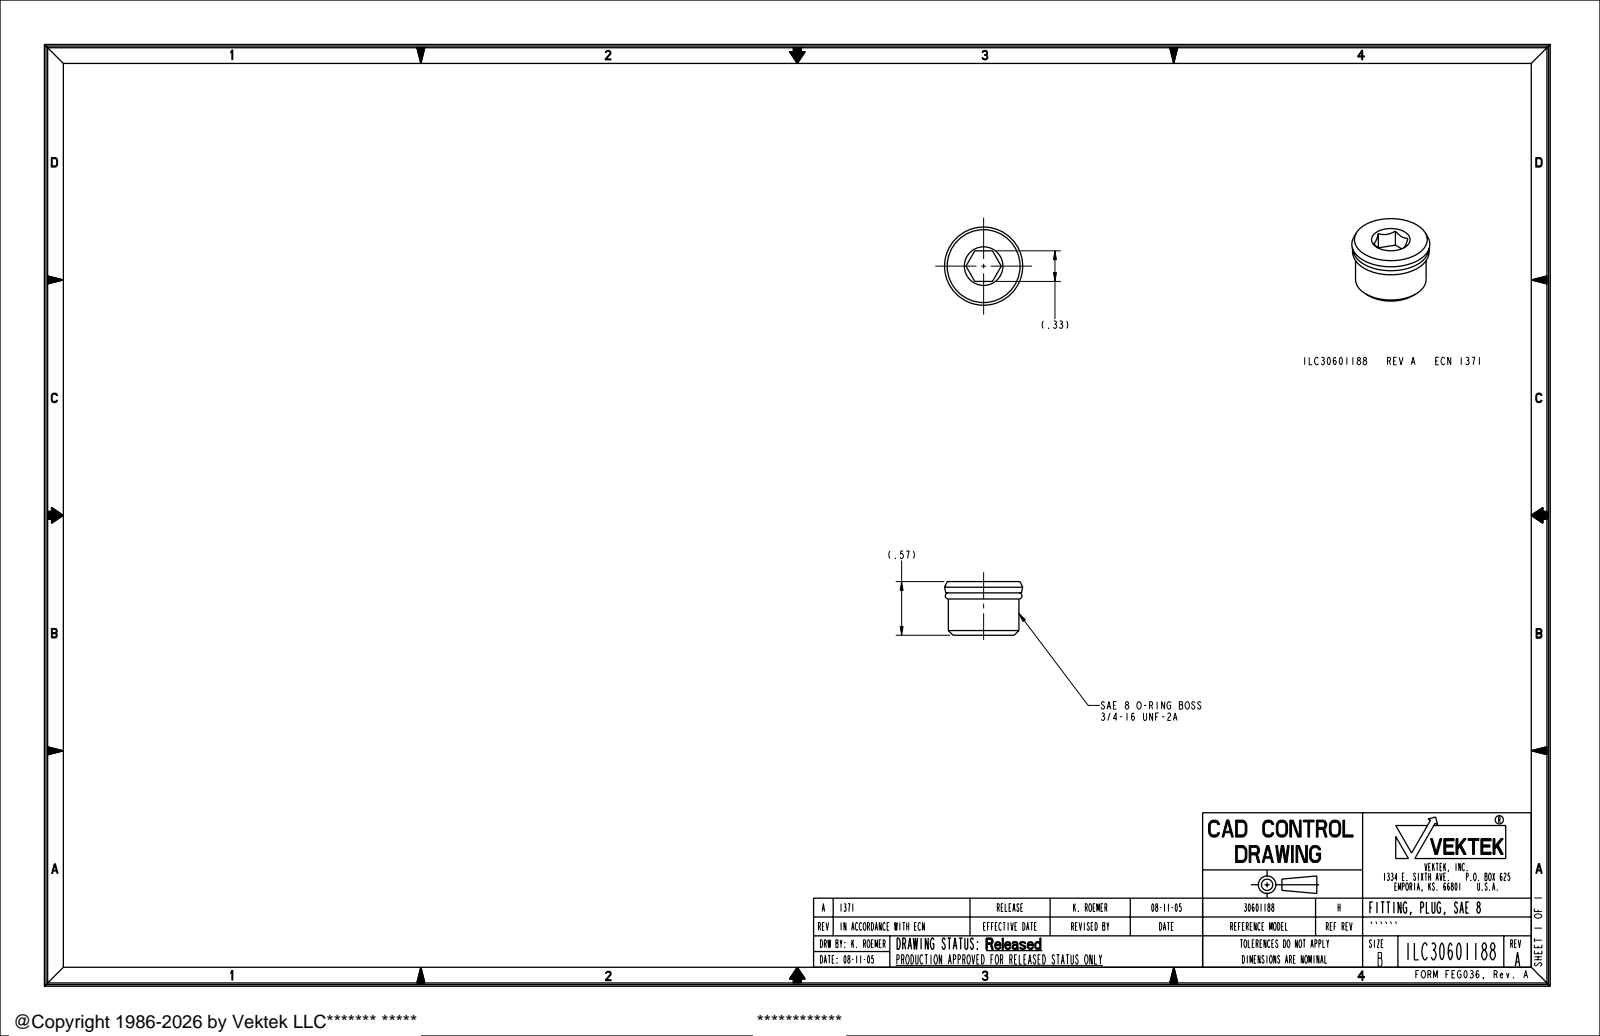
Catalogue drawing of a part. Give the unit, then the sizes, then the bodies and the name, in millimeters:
Units: millimetres
Overall size (bounding box): 21.1 × 21.1 × 14.5
Round bosses / shafts (diameter × count): ⌀19.1 ×1
Main face-to-face distances: 14.5, 8.3, 9.4, 5.1, 11.4, 2, 3
Volume: 3 980 mm³ · Surface area: 1 675 mm²
Bodies: 1 solid, 22 faces (10 planar, 2 cylindrical, 10 other)
Part name (STEP PRODUCT): ILC30601188
STEP written by: PRO/ENGINEER BY PARAMETRIC TECHNOLOGY CORPORATION, 2004290 (AUTOMOTIVE_DESIGN_CC2)
